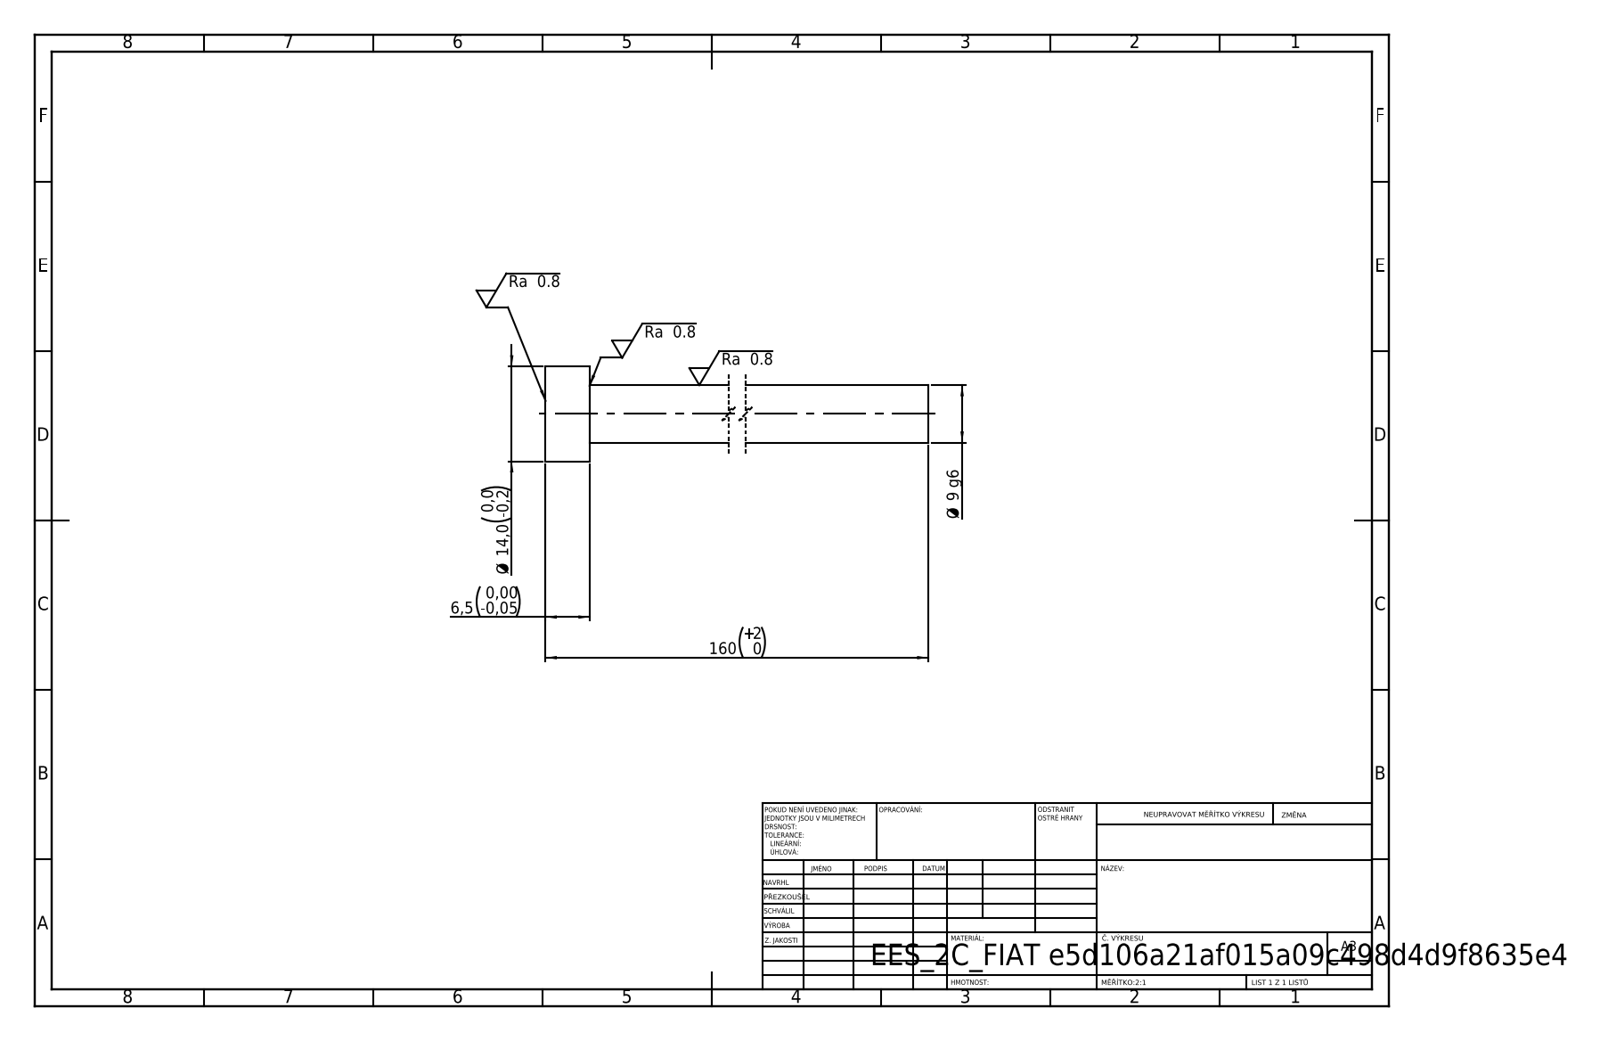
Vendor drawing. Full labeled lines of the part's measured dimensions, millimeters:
STEP written by: SolidWorks 2019 (CONFIG_CONTROL_DESIGN)
Units: millimetres
Bodies: 1 solid, 7 faces (3 planar, 4 cylindrical, 0 other)
Overall size (bounding box): 160 × 14 × 14
Volume: 9 711 mm³ · Surface area: 4 693 mm²
Round bosses / shafts (diameter × count): ⌀14 ×1, ⌀8.5 ×1
Main face-to-face distances: 6.5, 160, 153.5
